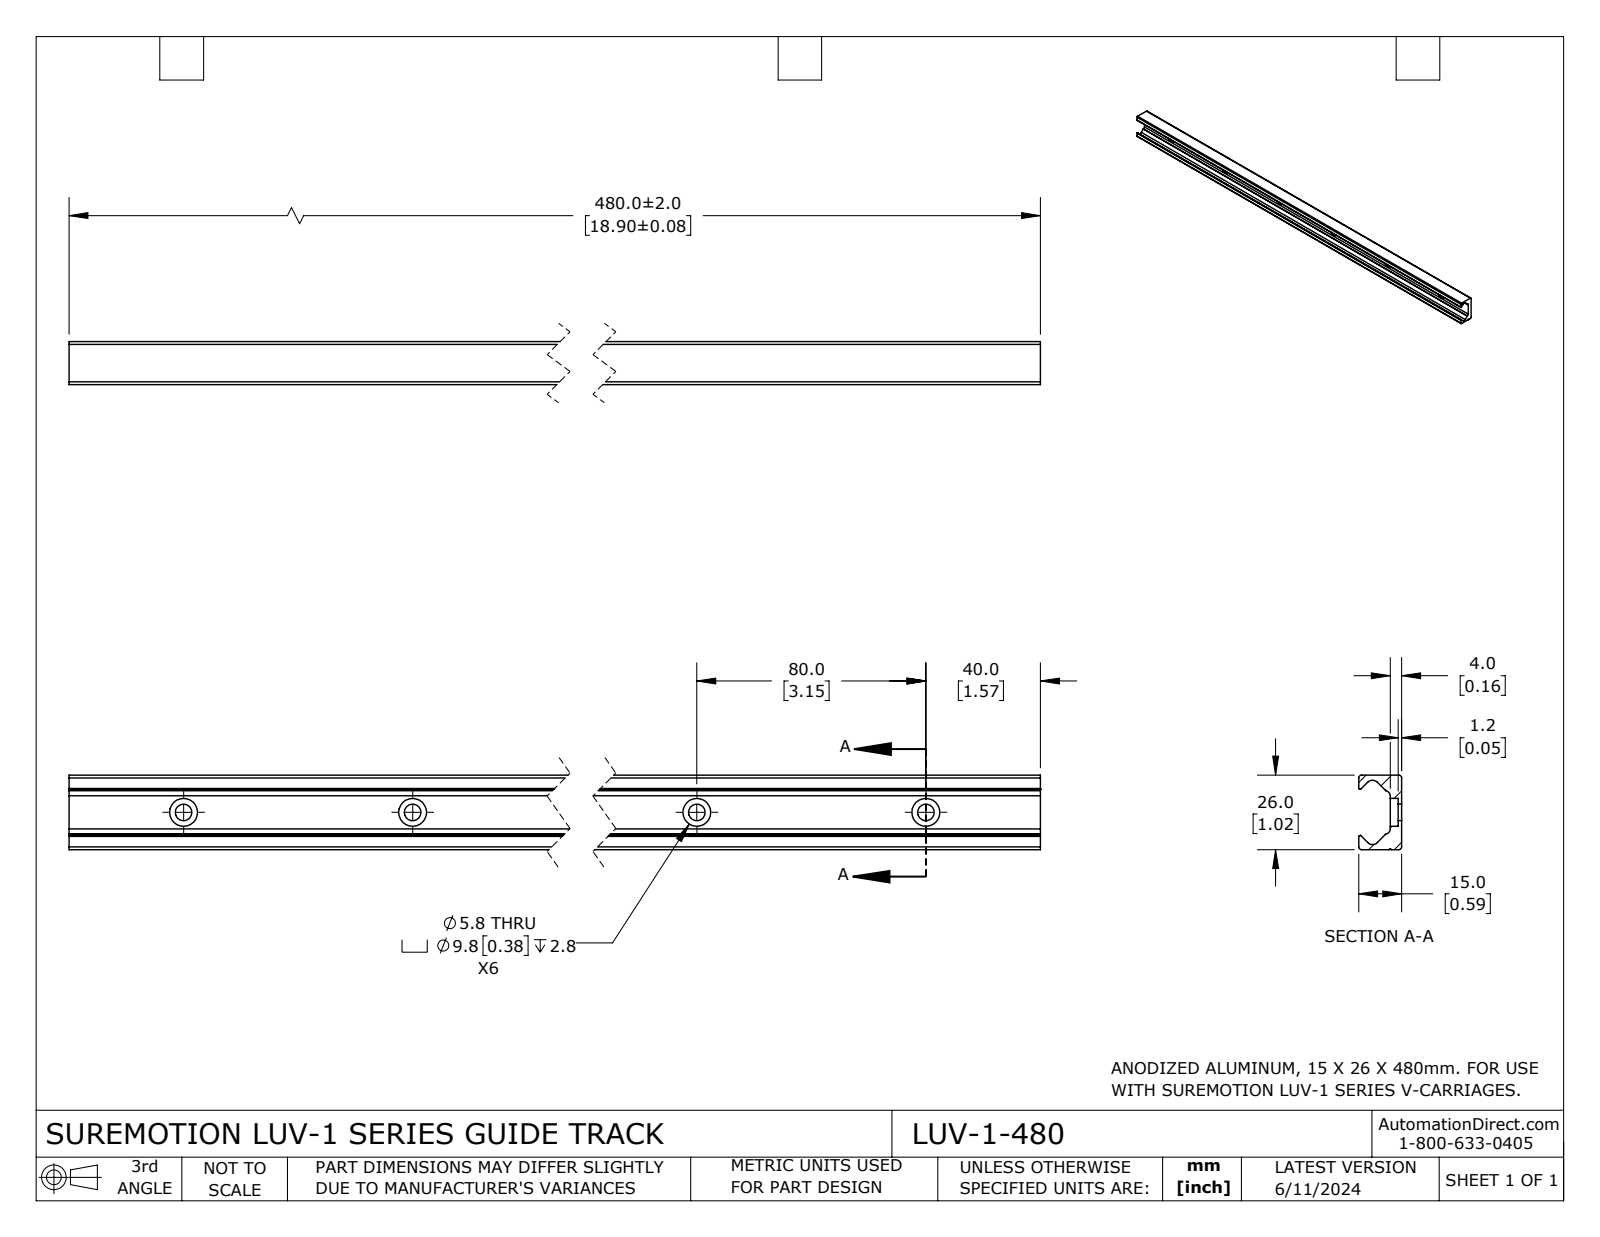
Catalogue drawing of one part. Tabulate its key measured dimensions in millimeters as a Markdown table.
| quantity | value |
| --- | --- |
| part name | LUV-1-480 |
| STEP written by | SolidWorks 2023 (CONFIG_CONTROL_DESIGN) |
| units | millimeters |
| bodies | 1 solid, 58 faces (19 planar, 39 cylindrical, 0 other) |
| overall size | 480 × 26.01 × 15.01 |
| volume | 86 429 mm³ |
| surface area | 51 143 mm² |
| round holes (diameter × count) | 5.79 × 6, 9.75 × 6 |
| partial cylindrical surfaces (radius × count) | 0.99 × 4, 0.51 × 2, 0.64 × 2, 0.76 × 2, 1.78 × 2, 2.39 × 2, 0.33 × 1 |
| main face-to-face distances | 26.02, 4.01, 15.02, 11.01, 17.27, 1.21, 2.8, 13.81, 480 |
| hole center spacings | 80, 160, 240, 320, 400 |
